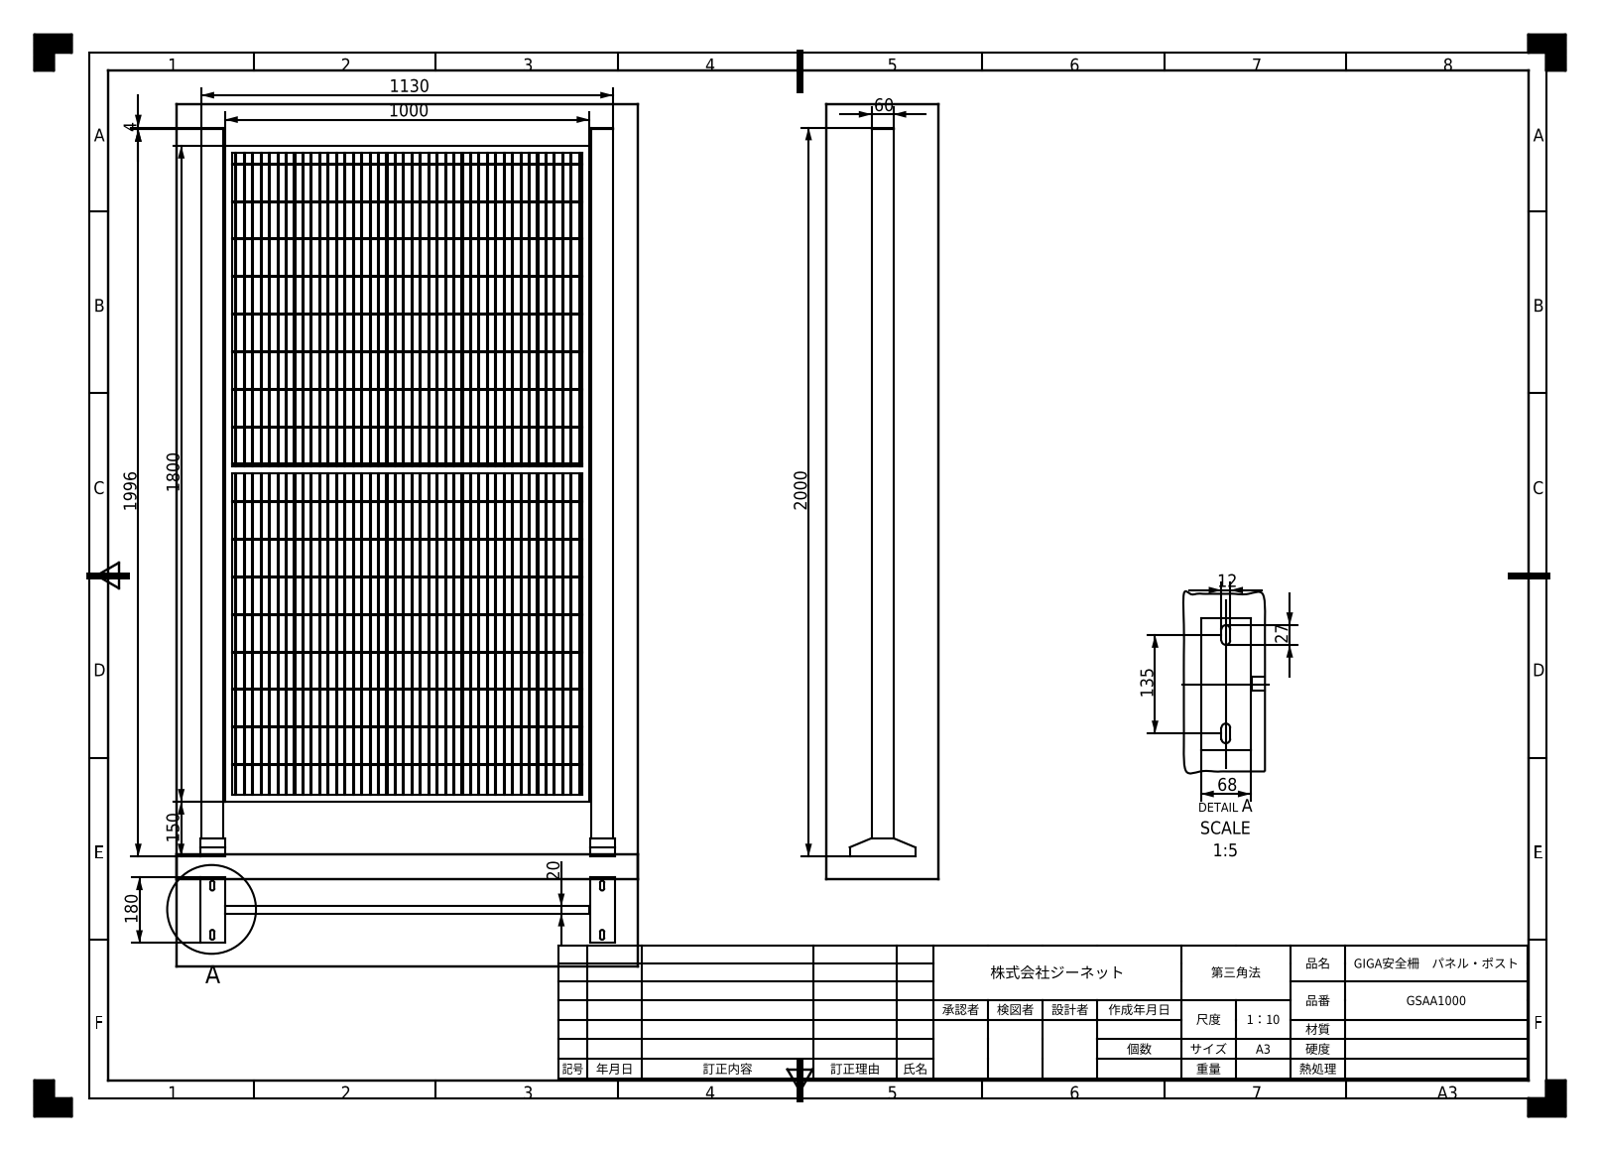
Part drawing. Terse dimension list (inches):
name: post_1000; GSAA1000_1; GSAA1000
written by: SIEMENS PLM Software NX 12.0 (AUTOMOTIVE_DESIGN)
unit: in
bodies: 64 solids, 249 faces (180 planar, 69 cylindrical, 0 other)
size: 78.74 × 44.803 × 7.087
volume: 1 116 in³; area: 3 753 in²
bosses: 59× ⌀0.118
rounds: 8× R0.236
face distances: 2.362, 42.126, 0.787, 1.55, 0.812, 0.763, 1.6, 44.488, 39.764, 2.559
